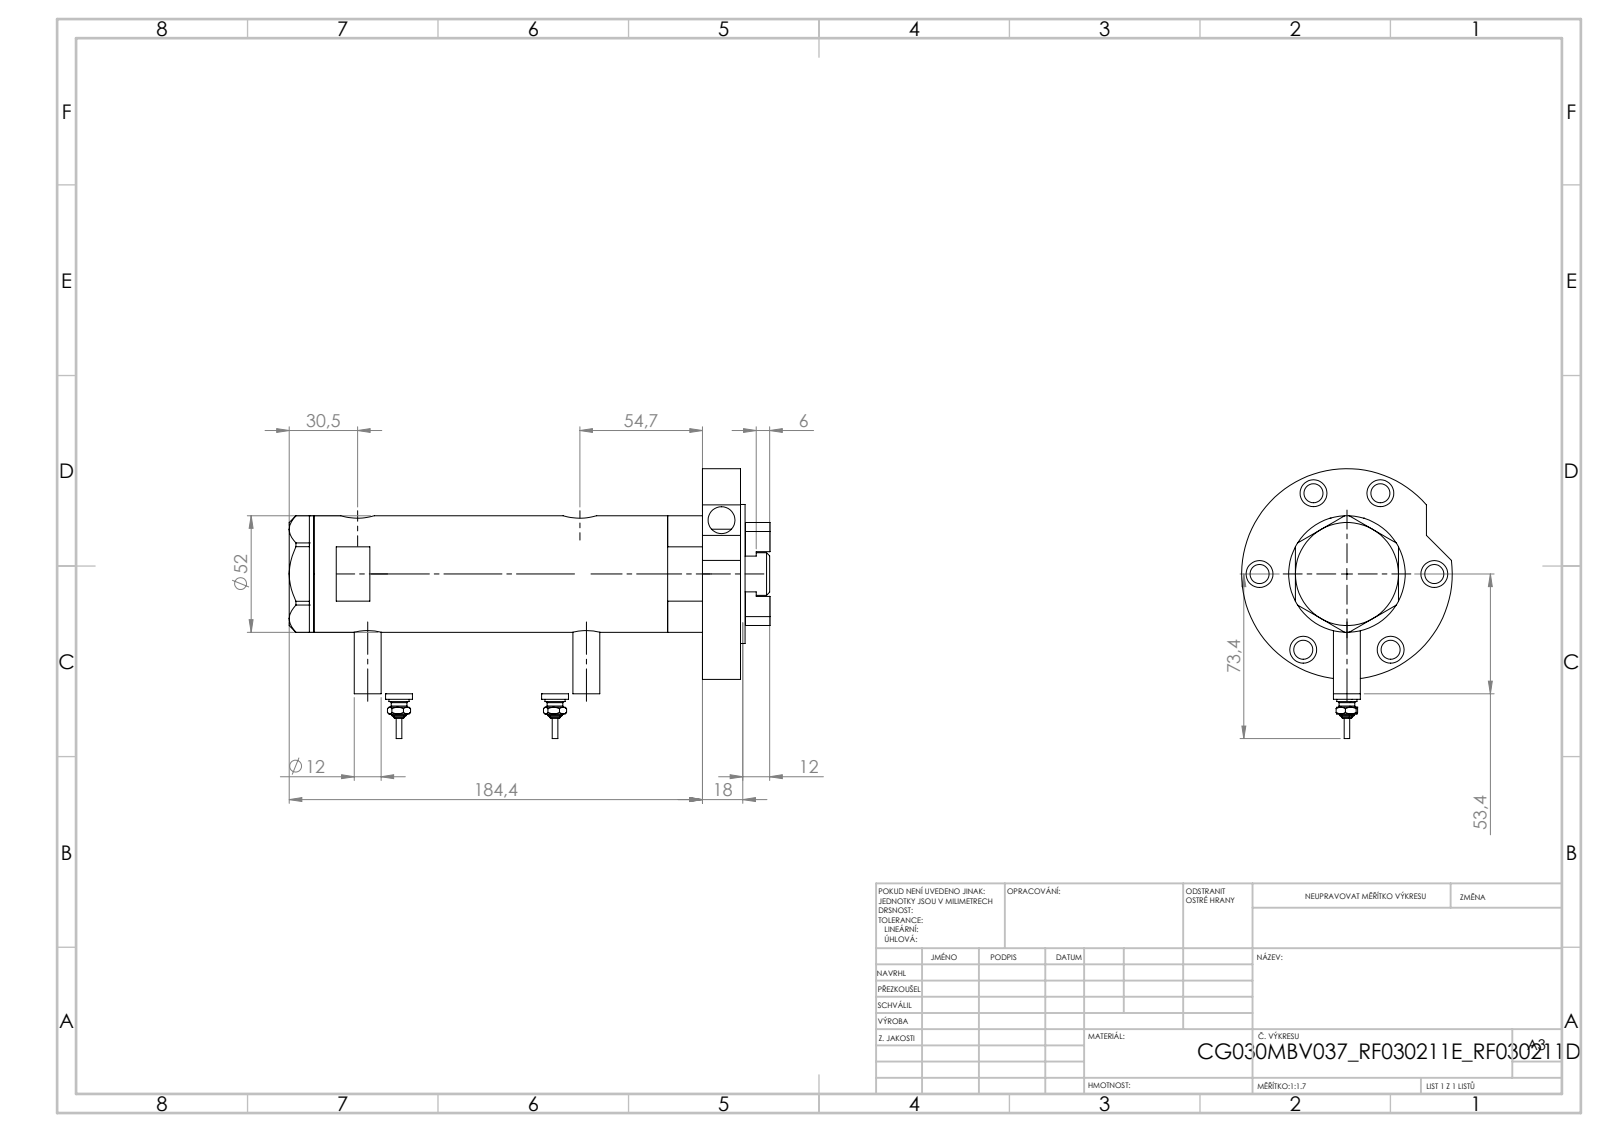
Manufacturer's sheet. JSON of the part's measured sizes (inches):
{"part_name": "V270CG_SWITCH; V270CG_RF211E; V270CG_RF211D; V270CG_MIDDLE (+3 more)", "step_written_by": "SolidWorks 2019 (CONFIG_CONTROL_DESIGN)", "units": "inches", "bodies": {"solids": 9, "faces": 330, "planar": 130, "cylindrical": 126, "other": 74}, "overall_size": [7.331, 4.146, 3.701], "volume_in3": 25.66, "surface_area_in2": 164.4, "round_holes": [[0.472, 7], [0.335, 6], [0.201, 4], [0.354, 4], [0.197, 2], [0.383, 2], [0.492, 2], [0.591, 2], [0.256, 1], [0.787, 1], [0.846, 1], [1.181, 1]], "round_bosses_or_shafts": [[0.472, 3], [0.354, 2], [0.276, 2], [0.171, 2], [0.094, 2], [3.701, 1], [2.441, 1], [2.047, 1]], "face_to_face_distances": [0.669, 5.609, 6.278, 0.079, 2.043, 6.357, 0.433, 3.565, 2.713, 2.791], "hole_center_spacings": [1.535, 0.659, 1.479, 1.843, 0.114, 0.177, 0.394, 0.881]}
